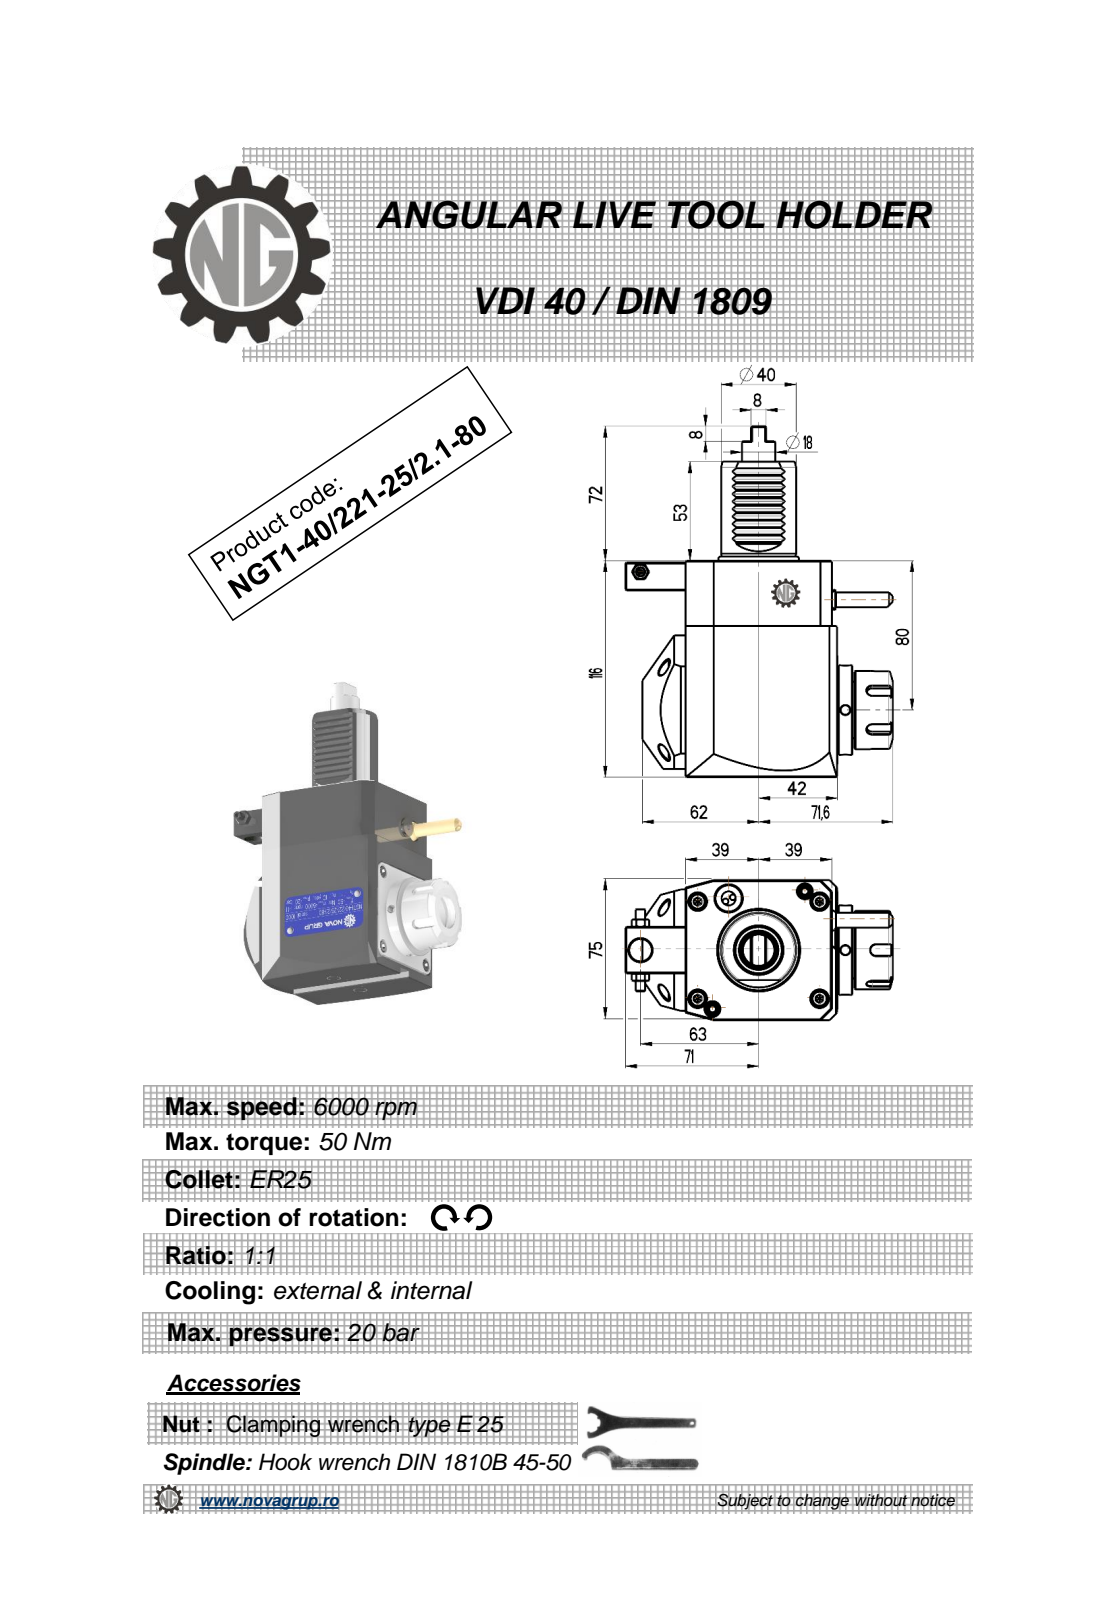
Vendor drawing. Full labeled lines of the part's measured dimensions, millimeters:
Part name (STEP PRODUCT): NGT1_40_221_25_2_1_80
STEP written by: PRO/ENGINEER BY PARAMETRIC TECHNOLOGY CORPORATION, 2010280 (CONFIG_CONTROL_DESIGN)
Units: millimetres
Bodies: 1 solid, 438 faces (200 planar, 89 cylindrical, 149 other)
Overall size (bounding box): 188 × 142.6 × 76.6
Volume: 866 709 mm³ · Surface area: 69 759 mm²
Round holes (diameter × count): ⌀5 ×3, ⌀3 ×1, ⌀4.2 ×1, ⌀9.5 ×1, ⌀12 ×1, ⌀20.3 ×1
Round bosses / shafts (diameter × count): ⌀48 ×1, ⌀42 ×1, ⌀40 ×1, ⌀38 ×1, ⌀33 ×1, ⌀17.8 ×1, ⌀11.2 ×1, ⌀8.96 ×1
Partial cylindrical surfaces — rounded edges, fillets, slot ends (radius × count): R0.26 ×12, R0.3 ×10, R0.22 ×6, R3 ×5, R0.8 ×2, R0.5 ×1, R40 ×1
Main face-to-face distances: 75, 116, 81, 3, 78, 80.8, 2.8, 112, 8, 25
Hole centre spacings: 20.93, 61.13, 72.5, 109.25, 131.95
